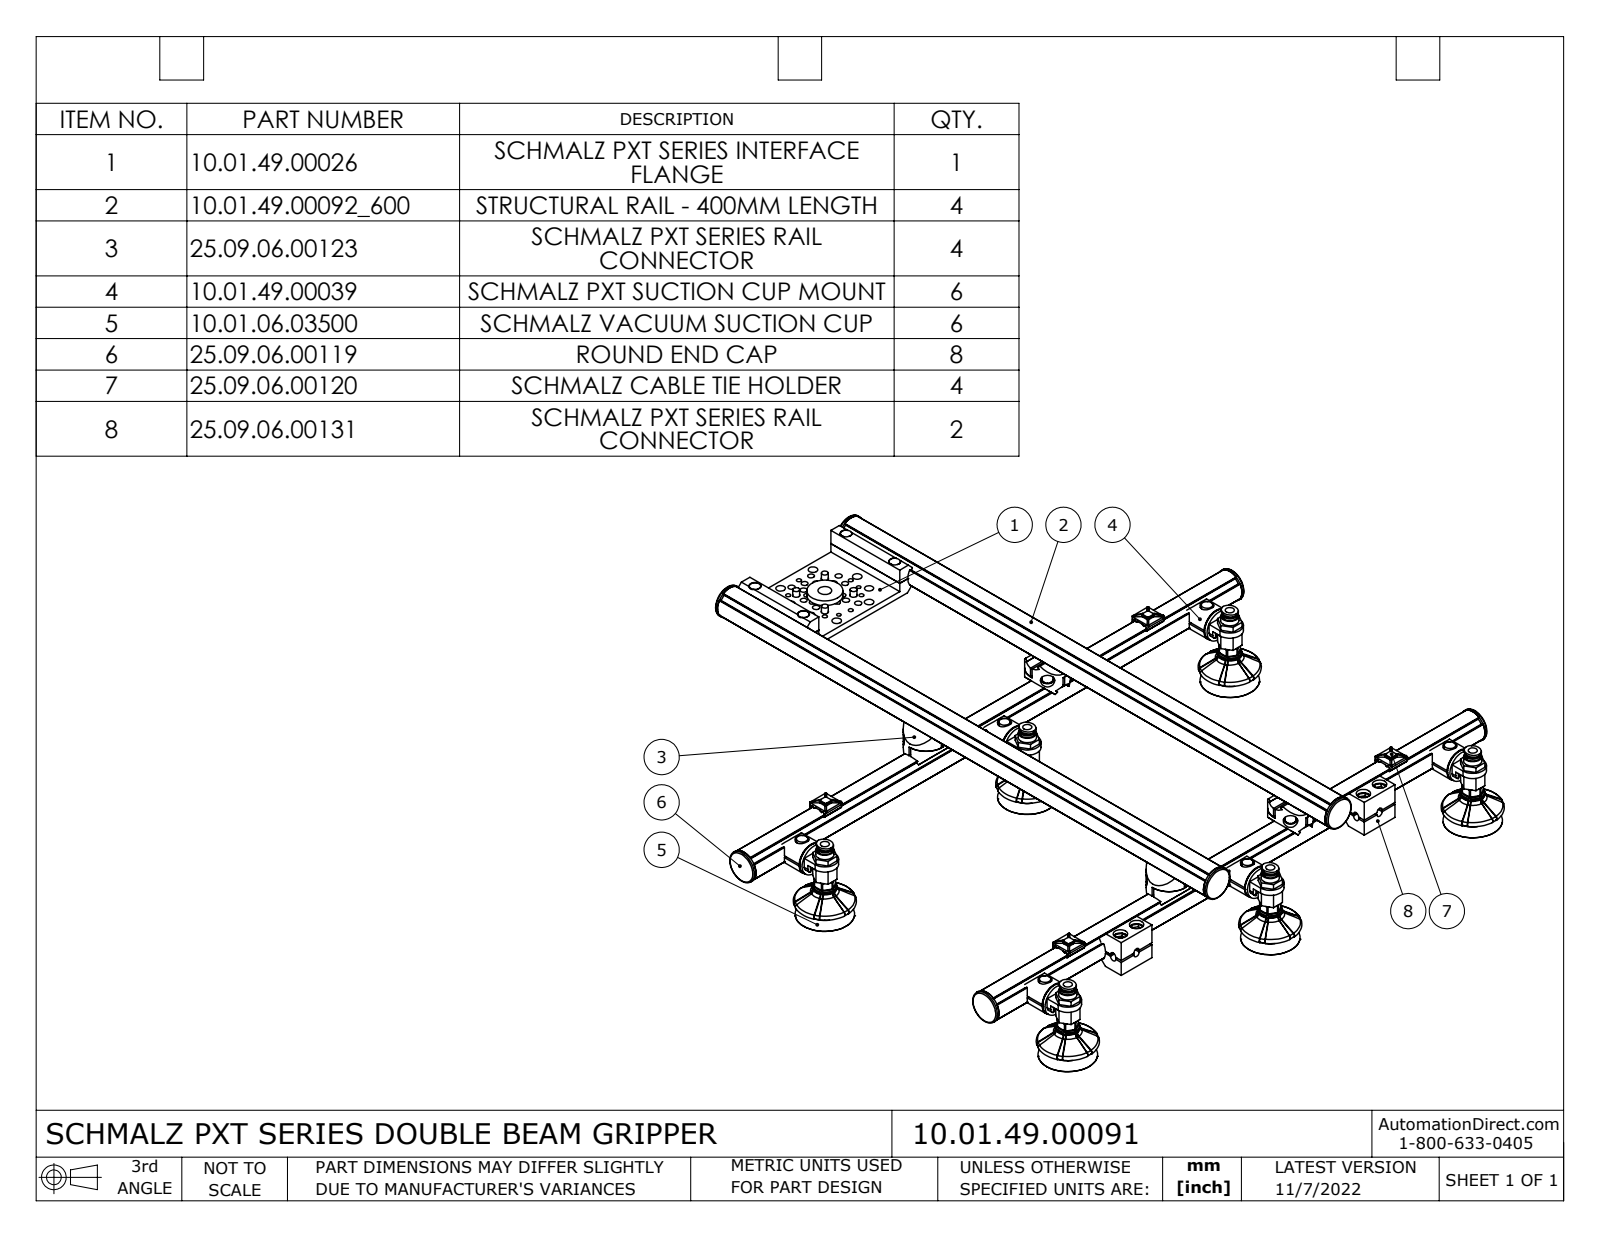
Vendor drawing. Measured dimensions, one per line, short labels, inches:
name: 10.01.49.00039; 10.01.49.00092_600; 10.01.49.00026; 25.09.06.00131 (+5 more)
written by: SolidWorks 2021 (CONFIG_CONTROL_DESIGN)
unit: in
bodies: 120 solids, 4233 faces (1811 planar, 1500 cylindrical, 922 other)
size: 24.526 × 23.858 × 4.536
volume: 65.61 in³; area: 1 241 in²
holes: 22× ⌀0.197, 12× ⌀0.252, 8× ⌀0.177, 8× ⌀0.315, 6× ⌀0.236, 6× ⌀0.24, 6× ⌀0.26, 6× ⌀0.276, 6× ⌀0.331, 6× ⌀0.351, 6× ⌀0.394, 6× ⌀0.402
bosses: 20× ⌀0.394, 20× ⌀0.236, 8× ⌀0.827, 7× ⌀1.181, 6× ⌀0.669, 6× ⌀0.63, 6× ⌀0.551, 6× ⌀0.545
rounds: 104× R0.012, 64× R0.016, 32× R0.059, 12× R0.02, 12× R0.039, 10× R0.492, 6× R0.126, 6× R0.197
face distances: 0.244, 0.059, 0.303, 8.35, 0.118, 11.811, 0.236, 0.362, 1.909, 3.355
hole spacings: 1.575, 1.722, 2.01, 1.26, 0.794, 0.964, 2.328, 0.484
